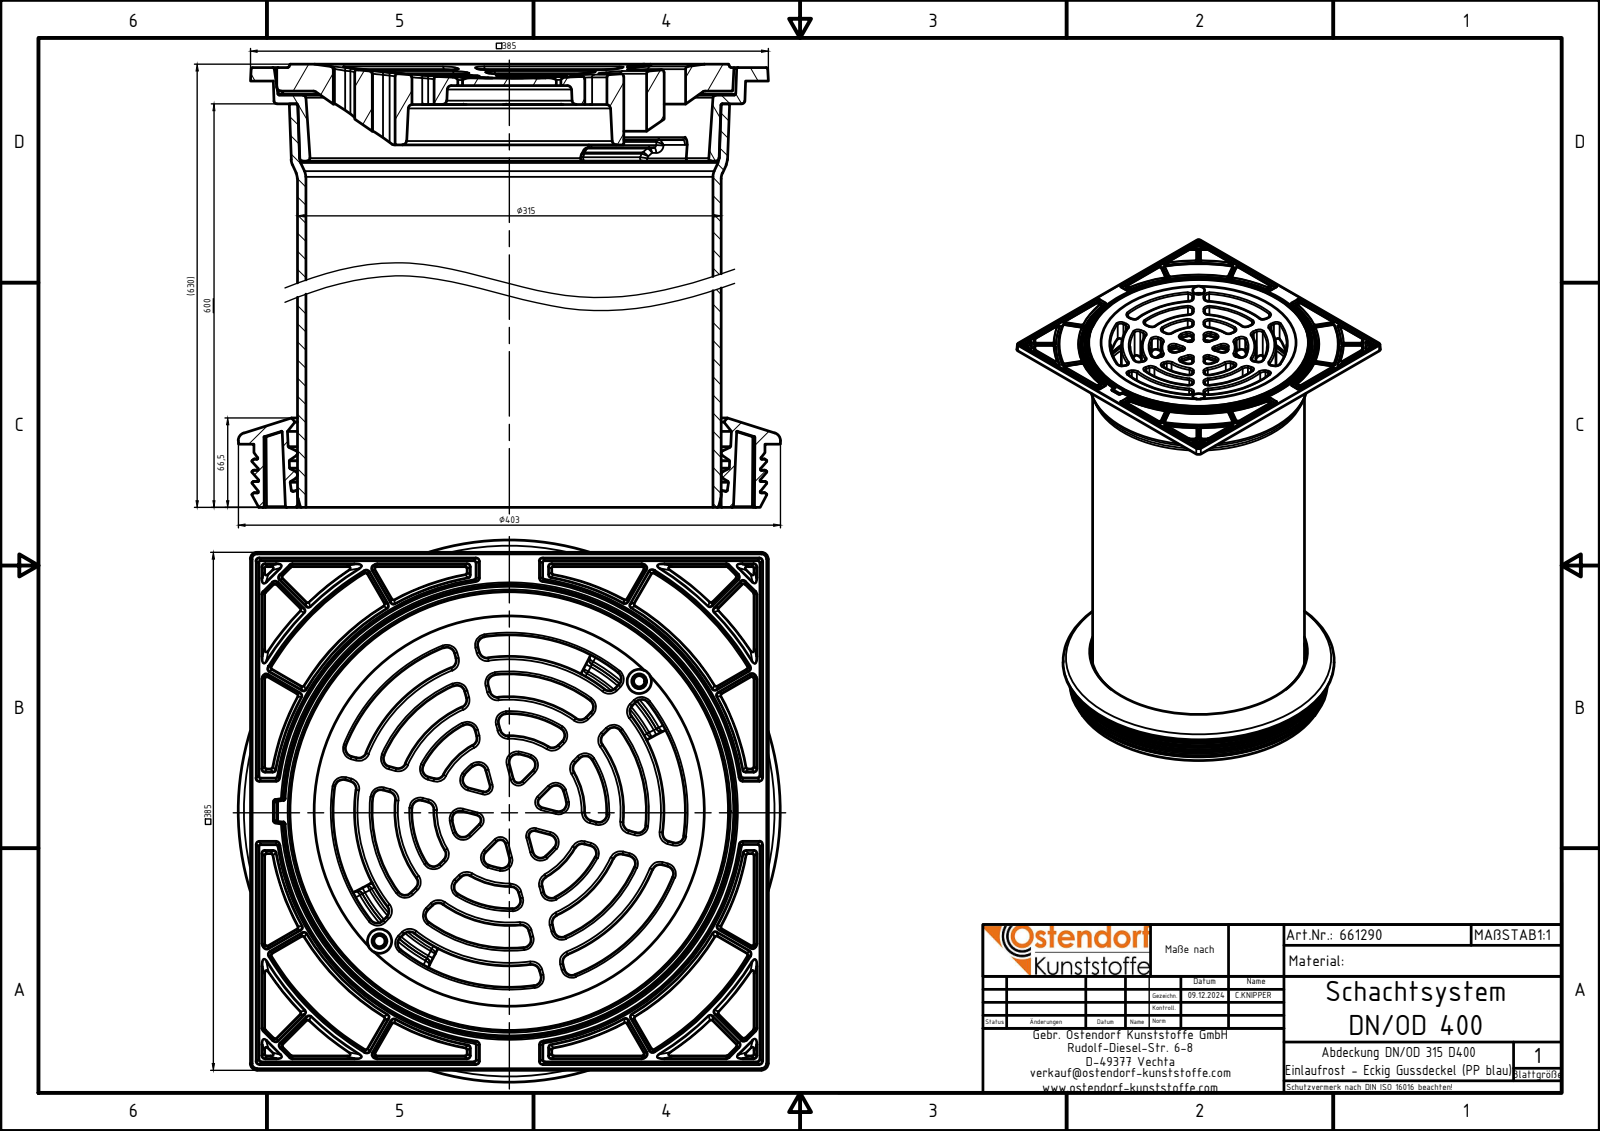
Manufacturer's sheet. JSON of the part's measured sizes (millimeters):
{"part_name": "661290z; 660300z; 660500z; 990060z (+2 more)", "step_written_by": "Autodesk Inventor 2024 (AUTOMOTIVE_DESIGN)", "units": "millimeters", "bodies": {"solids": 4, "faces": 1586, "planar": 235, "cylindrical": 431, "other": 920}, "overall_size": [612.5, 403, 403], "volume_mm3": 7698000, "surface_area_mm2": 2173000, "round_holes": [[8.38, 2], [11, 2], [18, 2], [302.6, 1], [315, 1]], "round_bosses_or_shafts": [[403, 1], [380, 1]], "partial_cylinders_radius": [[1, 192], [6, 84], [2.5, 48], [4, 14], [2, 4], [3, 1], [43, 1], [56, 1]], "face_to_face_distances": [10, 7.5, 17.5, 2.5, 20, 12.5, 17, 9.5, 27, 29.5], "hole_center_spacings": [136.5, 273]}
